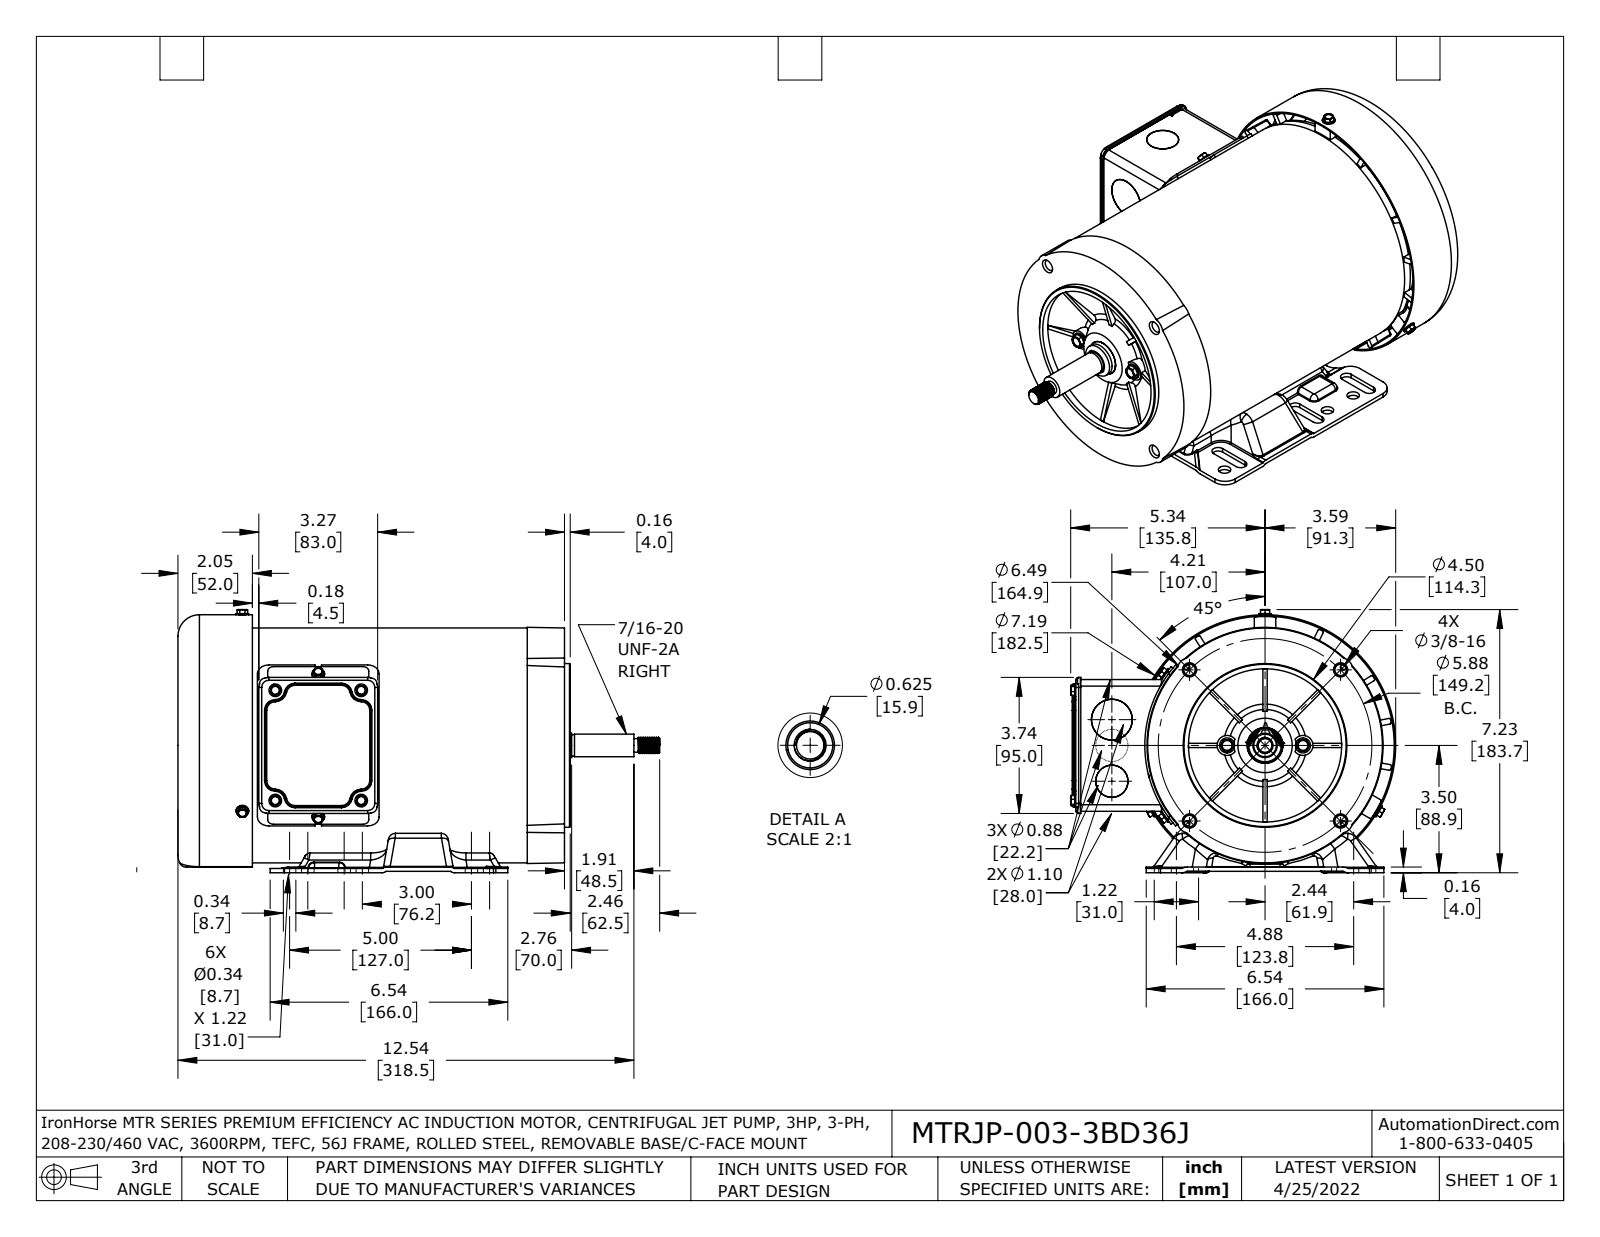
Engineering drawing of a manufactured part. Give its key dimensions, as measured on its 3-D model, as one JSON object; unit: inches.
{"part_name": "MTRJP-003-3BD36J redcmb1 coord fxt", "step_written_by": "SolidWorks 2021 (AUTOMOTIVE_DESIGN)", "units": "inches", "bodies": {"solids": 29, "faces": 2729, "planar": 658, "cylindrical": 899, "other": 1172}, "overall_size": [13.248, 8.938, 7.234], "volume_in3": 48.42, "surface_area_in2": 935.1, "round_holes": [[0.197, 10], [0.219, 9], [0.276, 8], [0.136, 7], [0.217, 6], [0.328, 6], [0.344, 6], [0.15, 4], [0.177, 4], [0.313, 4], [0.134, 2], [0.273, 2]], "round_bosses_or_shafts": [[0.164, 9], [0.348, 8], [0.236, 6], [0.414, 2], [0.19, 2], [7.185, 1], [4.5, 1], [0.945, 1]], "partial_cylinders_radius": [[0.118, 109], [0.039, 65], [0.157, 32], [0.02, 30], [0.138, 26], [0.079, 18], [0.276, 18], [0.172, 12]], "face_to_face_distances": [0.039, 0.118, 0.063, 0.157, 10.63, 10.591, 0.079, 3.559, 3.087, 0.047], "hole_center_spacings": [4.221, 3.031, 0.094, 2.32, 2.409, 2.937, 2.979, 3.748]}
